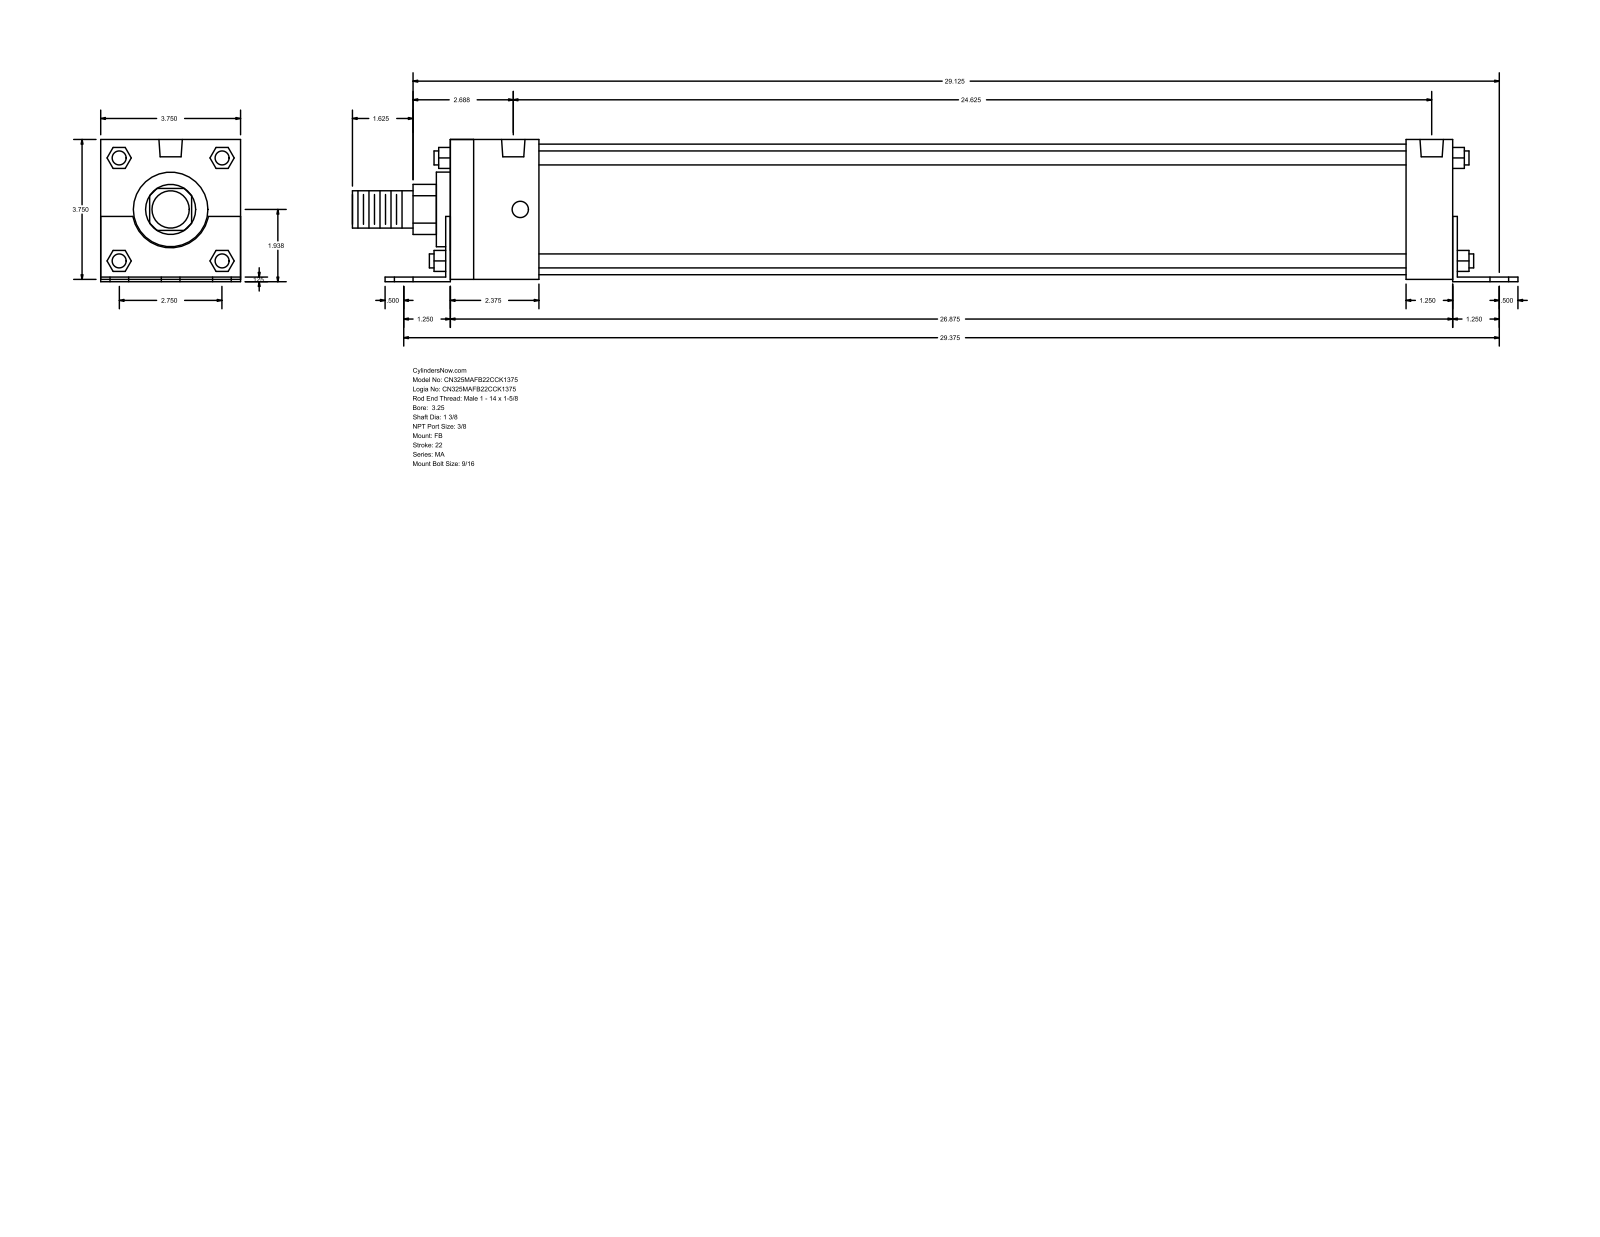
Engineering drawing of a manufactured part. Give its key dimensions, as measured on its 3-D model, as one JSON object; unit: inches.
{"part_name": "MA_FB__0325_1.375", "step_written_by": "GSSL Pune (CONFIG_CONTROL_DESIGN)", "units": "inches", "bodies": {"solids": 0, "faces": 140, "planar": 105, "cylindrical": 35, "other": 0}, "overall_size": [31.25, 3.813, 3.75], "round_holes": [[0.563, 6], [0.437, 4], [0.627, 2]], "round_bosses_or_shafts": [[0.375, 4], [3.5, 1], [2, 1], [1.375, 1], [1, 1]], "partial_cylinders_radius": [[0.672, 1], [1.03, 1]], "face_to_face_distances": [3.75, 0.125, 0.063, 3.812, 0.062, 3.687, 0.125, 26.875, 27, 1.25], "hole_center_spacings": [1.375, 29.407, 29.375, 2.275, 2.427, 2.75, 3.243, 3.414]}
